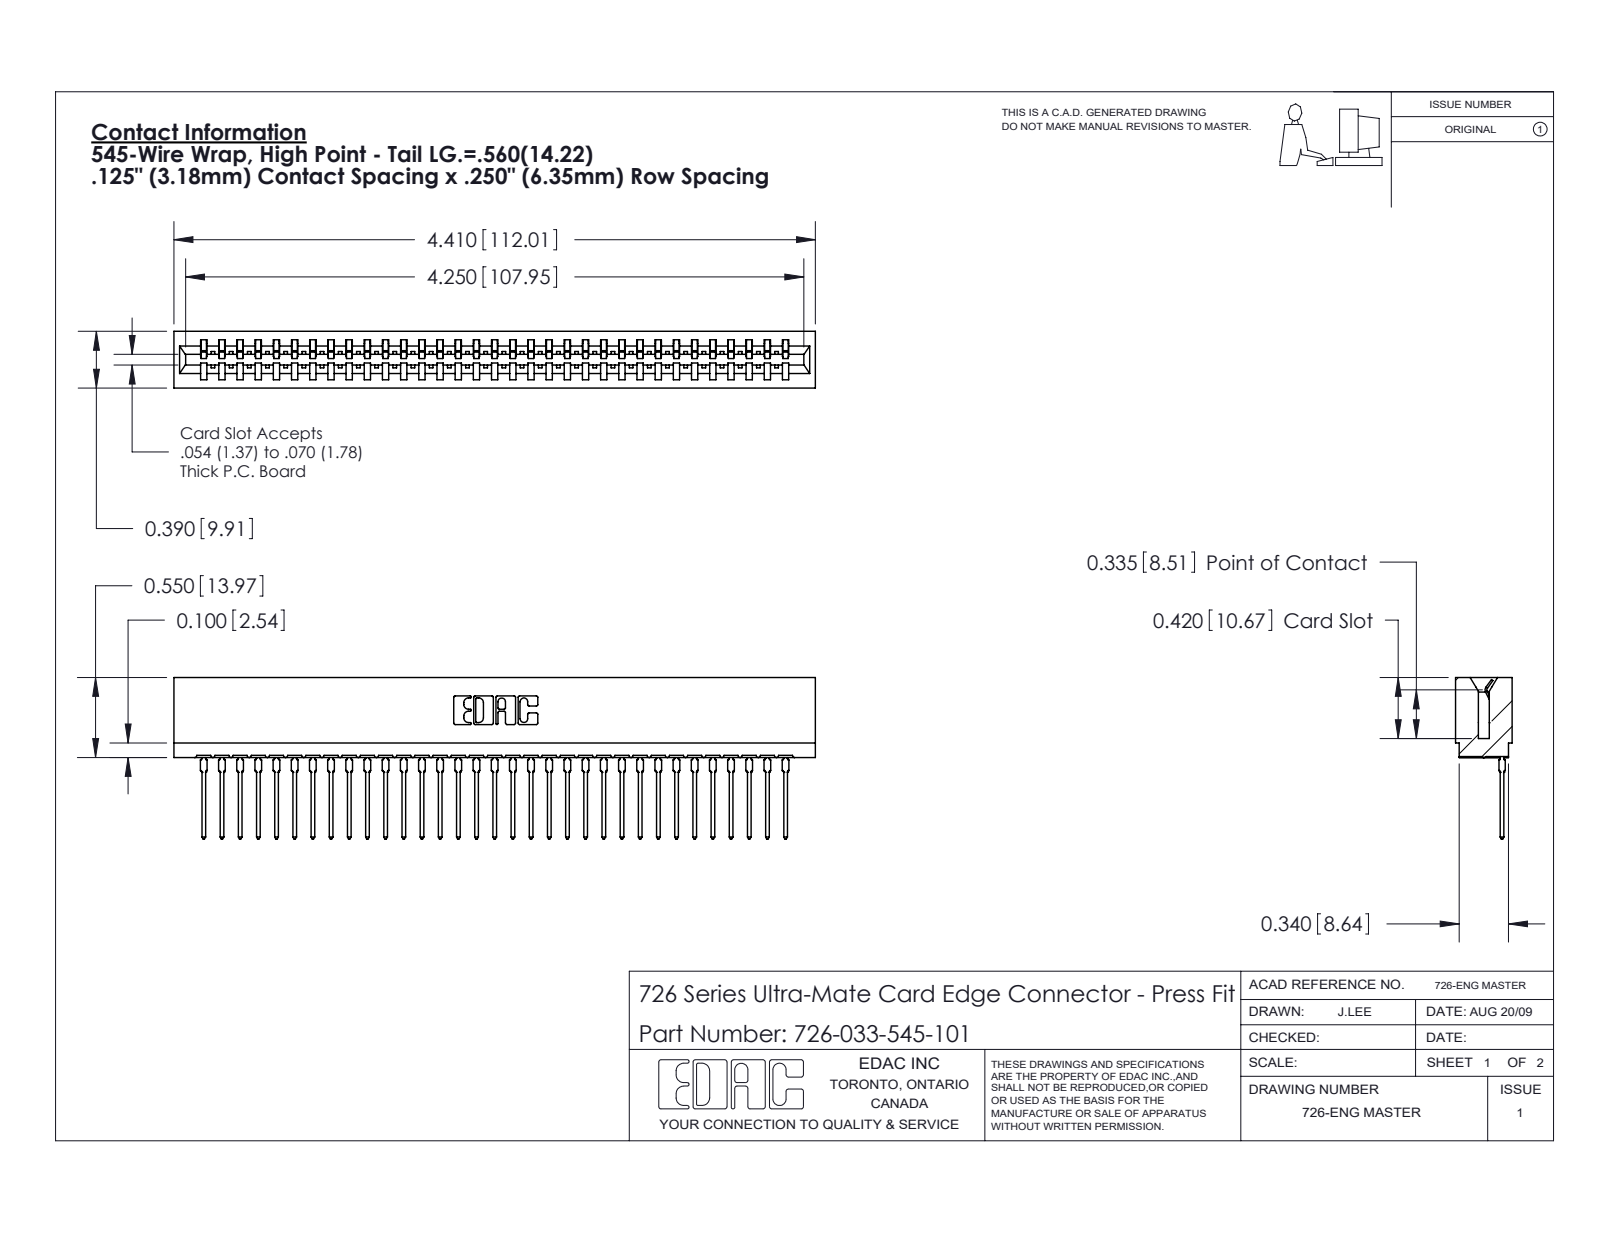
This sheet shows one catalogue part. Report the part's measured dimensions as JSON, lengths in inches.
{"part_name": "746-292-001_545; 726-033-545-101; 726 Part_.515 Slot Depth - 01", "step_written_by": "SolidWorks 2020 (CONFIG_CONTROL_DESIGN)", "units": "inches", "bodies": {"solids": 34, "faces": 3661, "planar": 2134, "cylindrical": 669, "other": 858}, "overall_size": [4.41, 1.109, 0.39], "volume_in3": 0.619, "surface_area_in2": 24.51, "partial_cylinders_radius": [[0.021, 66], [0.015, 34], [0.01, 22], [0.007, 6], [0.031, 6], [0.005, 4], [0.011, 4], [0.026, 3]], "face_to_face_distances": [0.057, 0.333, 0.25, 0.39, 0.025, 0.307, 0.083, 0.5, 0.275, 0.75]}
